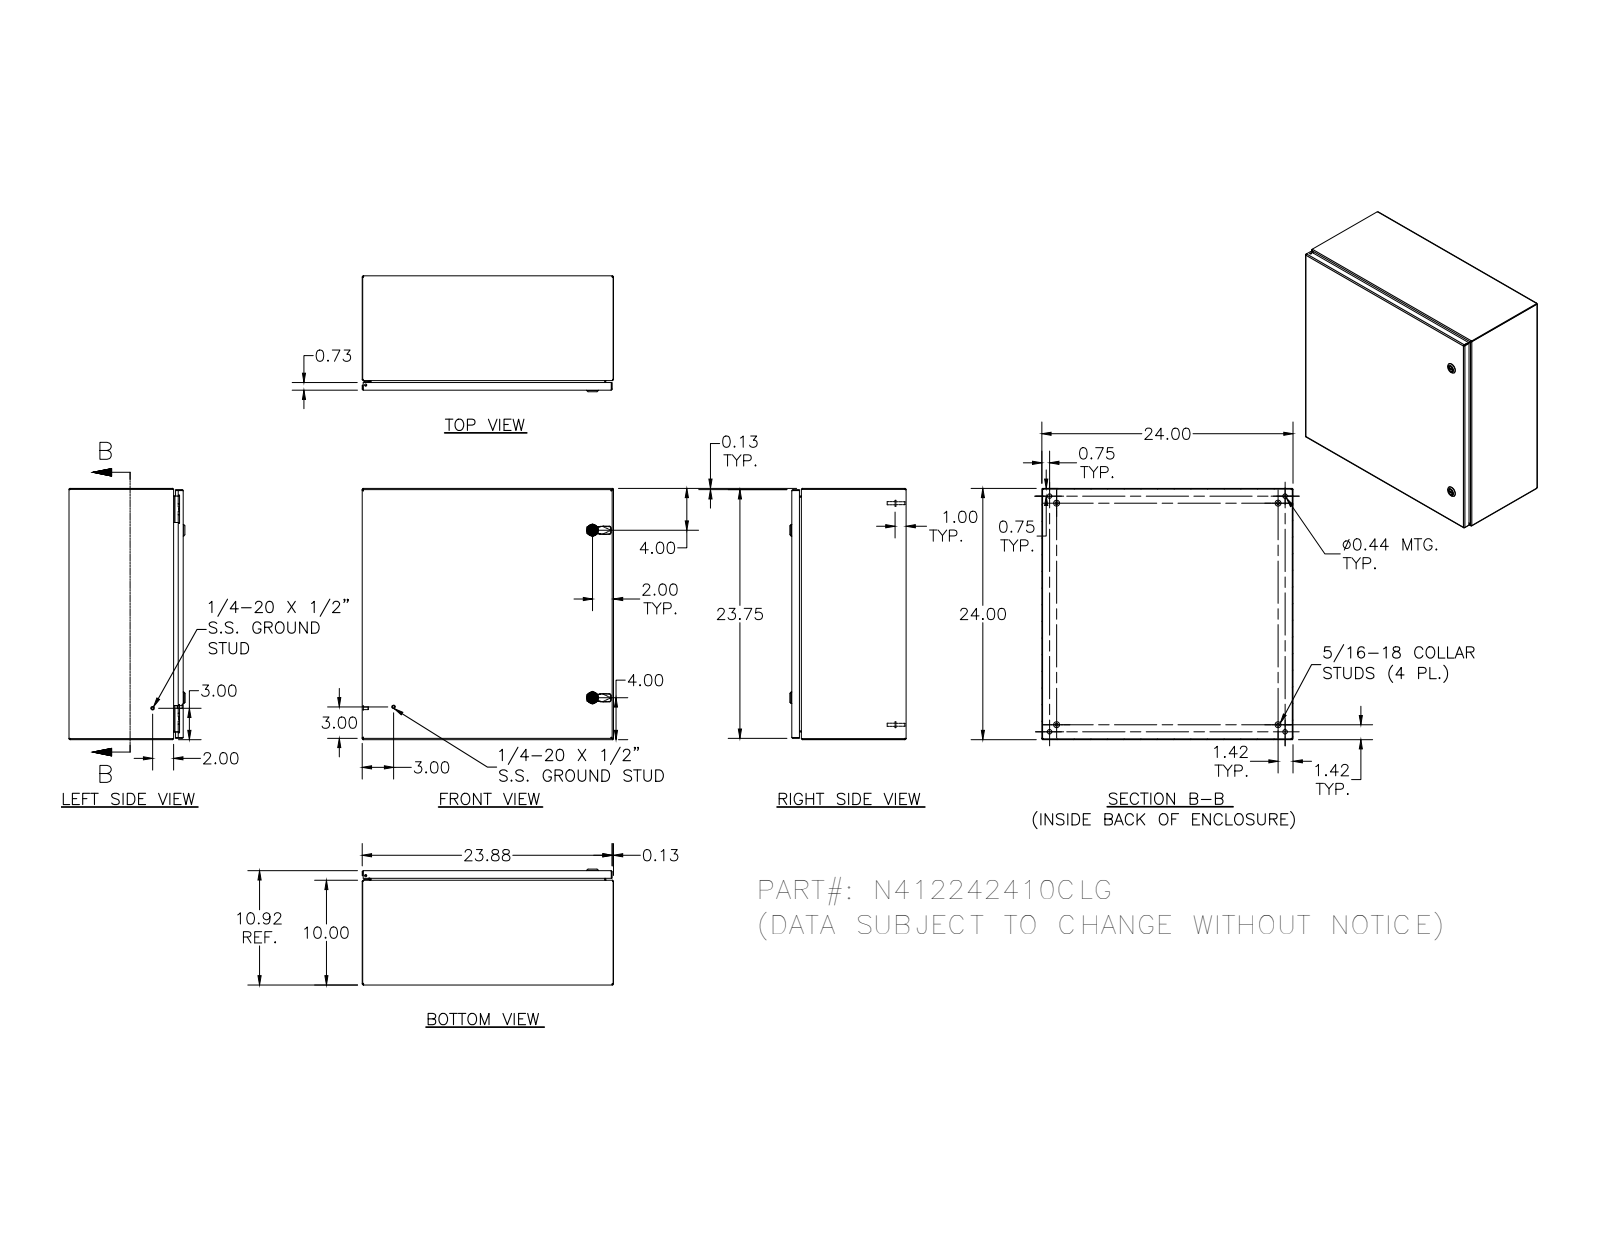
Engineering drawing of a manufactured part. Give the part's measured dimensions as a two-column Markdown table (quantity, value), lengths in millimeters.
| quantity | value |
| --- | --- |
| part name | N412242410CLG |
| STEP written by | SolidWorks 2018 (AUTOMOTIVE_DESIGN) |
| units | millimeters |
| bodies | 40 solids, 1812 faces (704 planar, 676 cylindrical, 432 other) |
| overall size | 609.6 × 609.6 × 281.3 |
| volume | 2 804 000 mm³ |
| surface area | 2 995 000 mm² |
| round holes (diameter × count) | 4.8 × 5, 2.4 × 4, 3.9 × 4, 4.2 × 4, 4.4 × 4, 11.1 × 4, 4 × 2, 5 × 2, 8 × 2, 10 × 2, 10.2 × 2, 16.1 × 2 |
| round bosses / shafts (diameter × count) | 6.4 × 10, 14.3 × 4, 9.1 × 4, 8.1 × 4, 7.6 × 4, 6.5 × 4, 4.2 × 4, 3.3 × 4 |
| partial cylindrical surfaces (radius × count) | 0.3 × 54, 0.8 × 30, 1.3 × 26, 0.5 × 23, 2.7 × 20, 0.4 × 18, 3.2 × 16, 0.8 × 8 |
| main face-to-face distances | 1.9, 275.4, 273.5, 277.3, 1.9, 607.7, 607.7, 605.8, 609.6, 23.3 |
| hole center spacings | 508, 16.8, 16.7, 33.2, 49.9, 491.2, 524.8, 571.5 |
